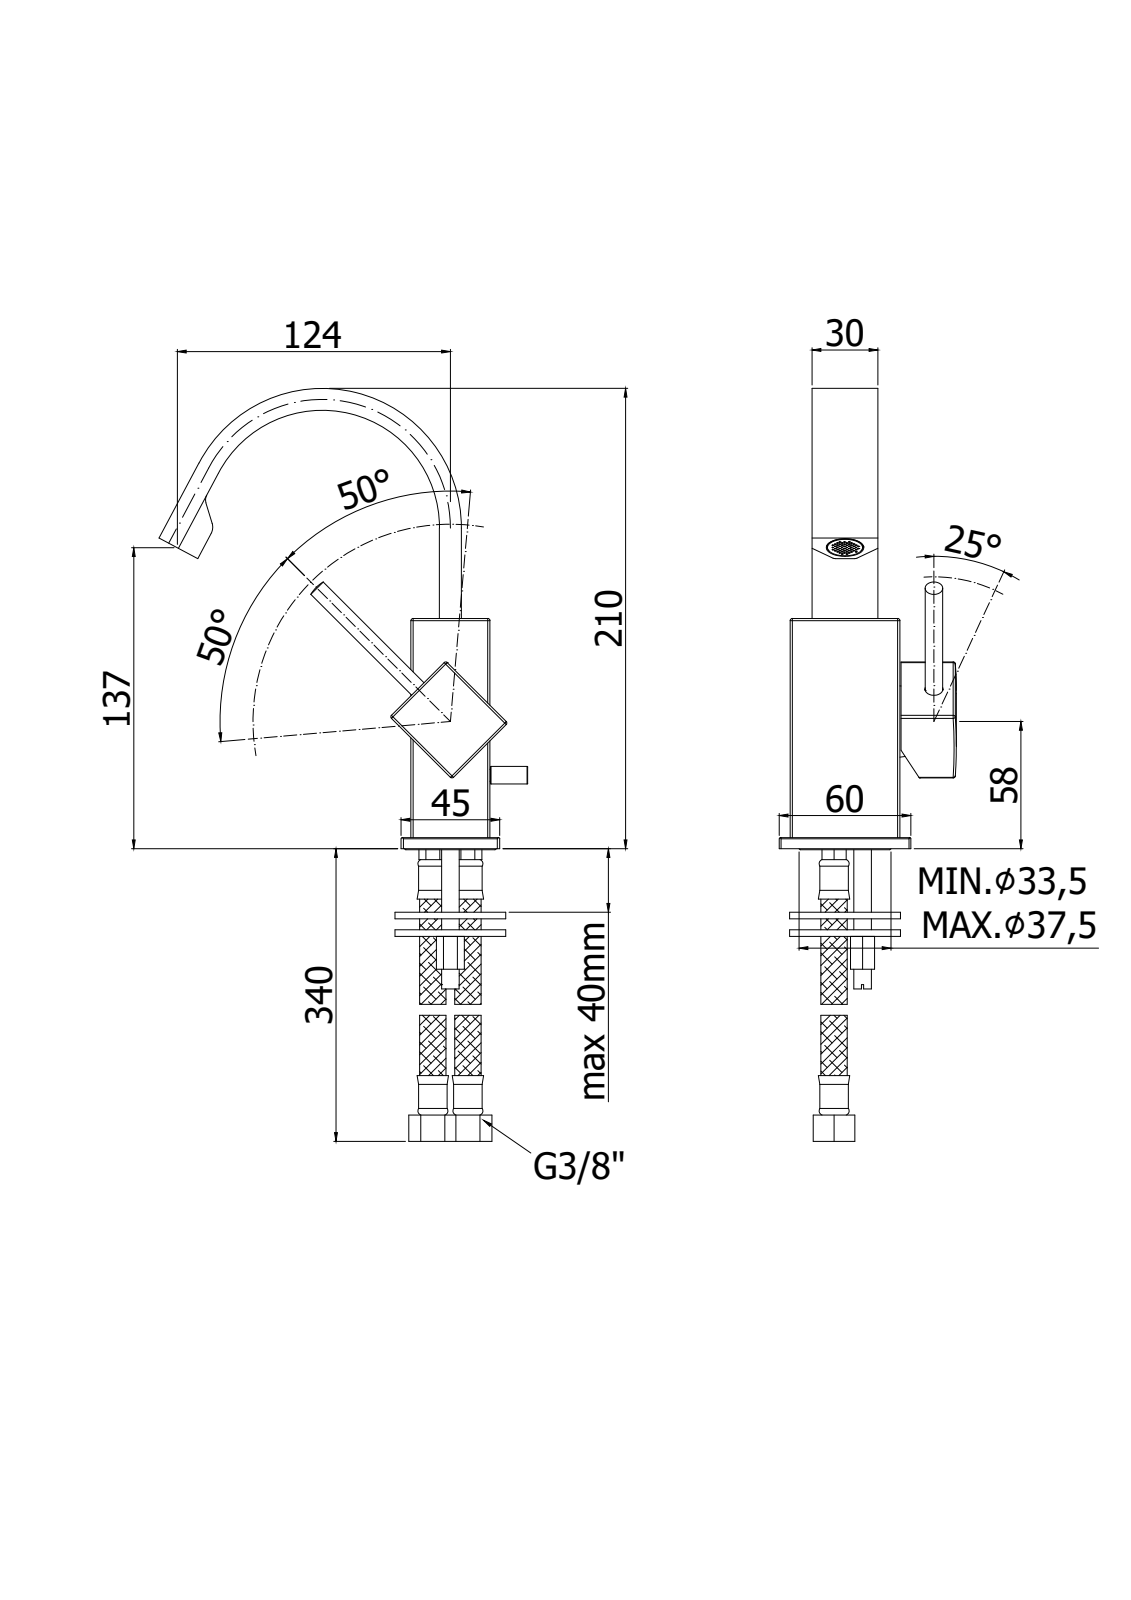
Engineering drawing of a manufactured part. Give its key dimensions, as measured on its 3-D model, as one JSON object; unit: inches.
{"part_name": "LEA838CR", "step_written_by": "CREO PARAMETRIC BY PTC INC, 2020044 (CONFIG_CONTROL_DESIGN)", "units": "inches", "bodies": {"solids": 0, "faces": 69, "planar": 27, "cylindrical": 26, "other": 16}, "overall_size": [8.465, 6.611, 3.267], "round_bosses_or_shafts": [[0.315, 1]], "partial_cylinders_radius": [[0.039, 8], [0.059, 4], [0.031, 2], [1.033, 1], [1.181, 1], [2.118, 1], [2.512, 1]], "face_to_face_distances": [0.394, 1.575, 1.417, 1.969, 0.197, 0.512, 0.906, 1.181, 4.134, 3.937]}
